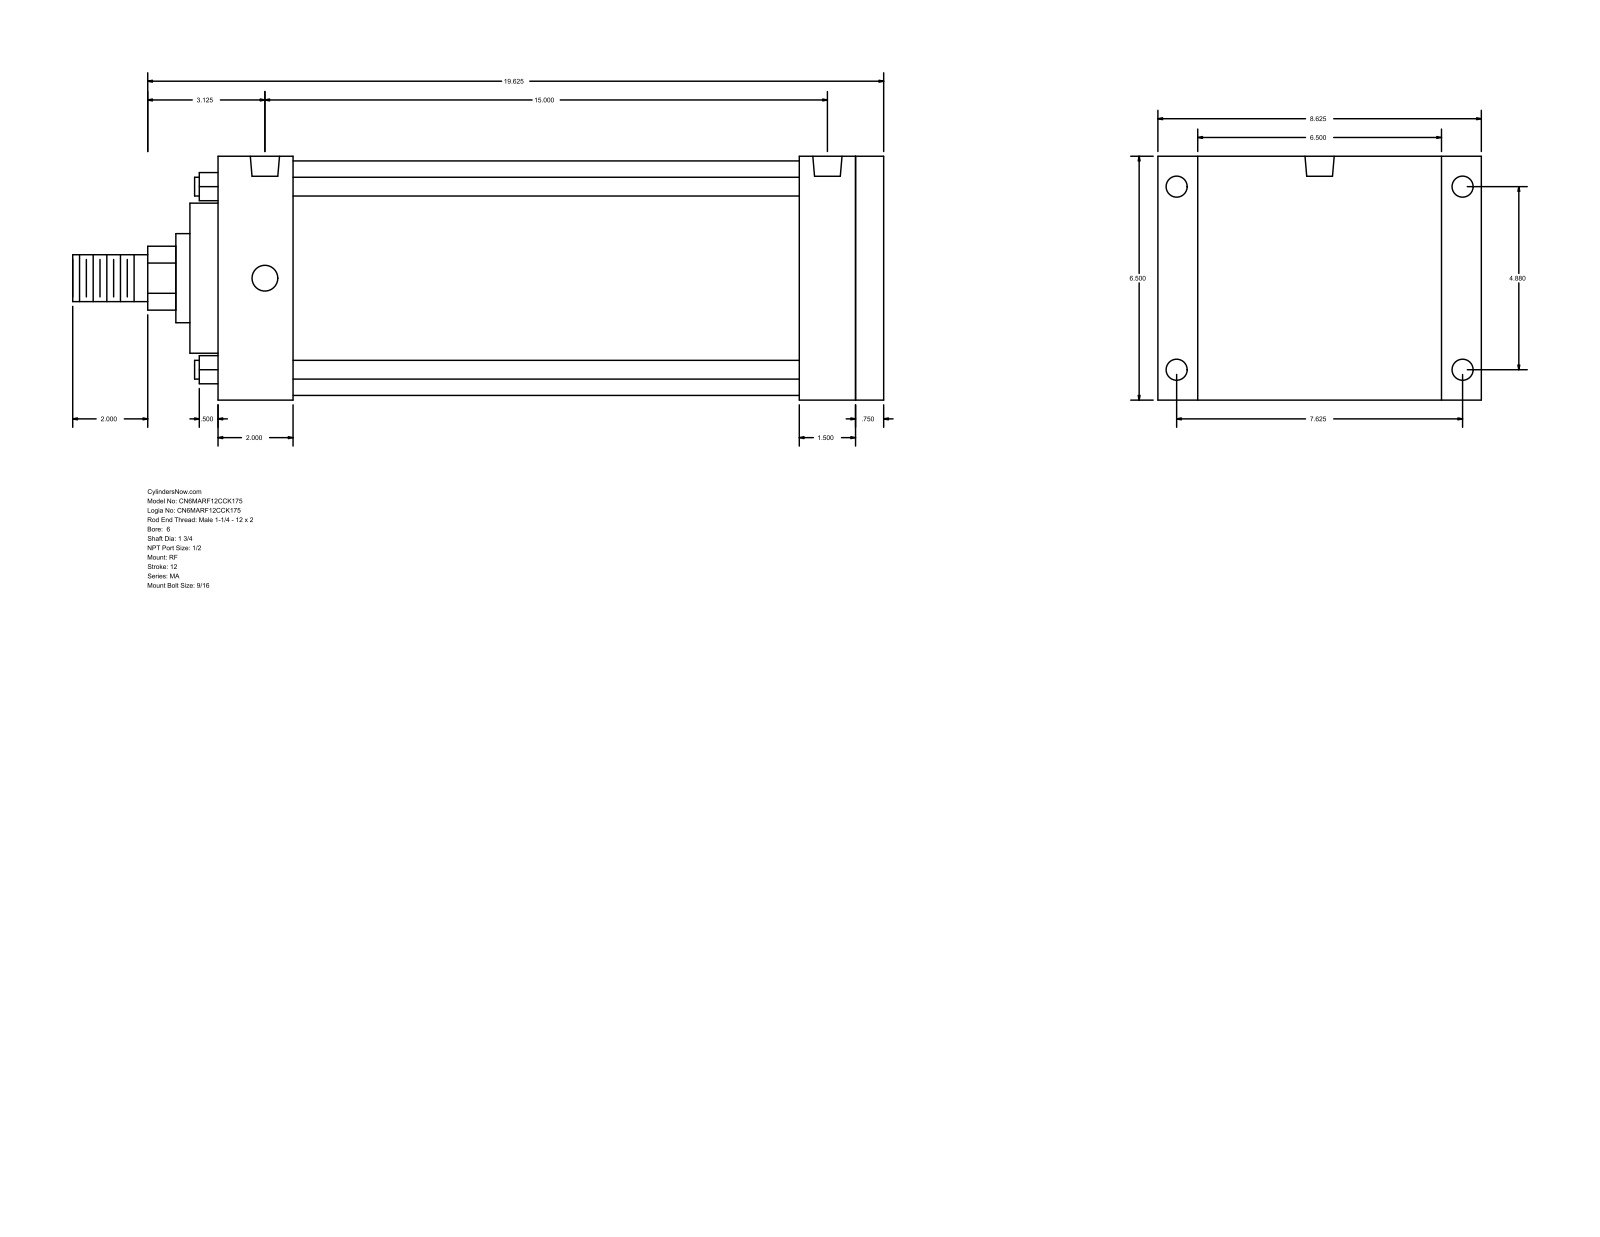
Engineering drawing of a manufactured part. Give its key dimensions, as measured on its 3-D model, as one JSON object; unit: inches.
{"part_name": "MA_RF__0600_1.75", "step_written_by": "GSSL Pune (CONFIG_CONTROL_DESIGN)", "units": "inches", "bodies": {"solids": 0, "faces": 94, "planar": 65, "cylindrical": 29, "other": 0}, "overall_size": [21.625, 8.625, 6.5], "round_holes": [[0.563, 4], [0.687, 4], [0.778, 2]], "round_bosses_or_shafts": [[0.5, 4], [6.25, 1], [4, 1], [2.375, 1], [1.75, 1], [1.25, 1]], "partial_cylinders_radius": [[0.852, 1]], "face_to_face_distances": [6.5, 17.75, 0.75, 17, 2, 15, 15.75, 15.5, 13.5, 1.5], "hole_center_spacings": [4.88, 7.625, 9.053, 15]}
